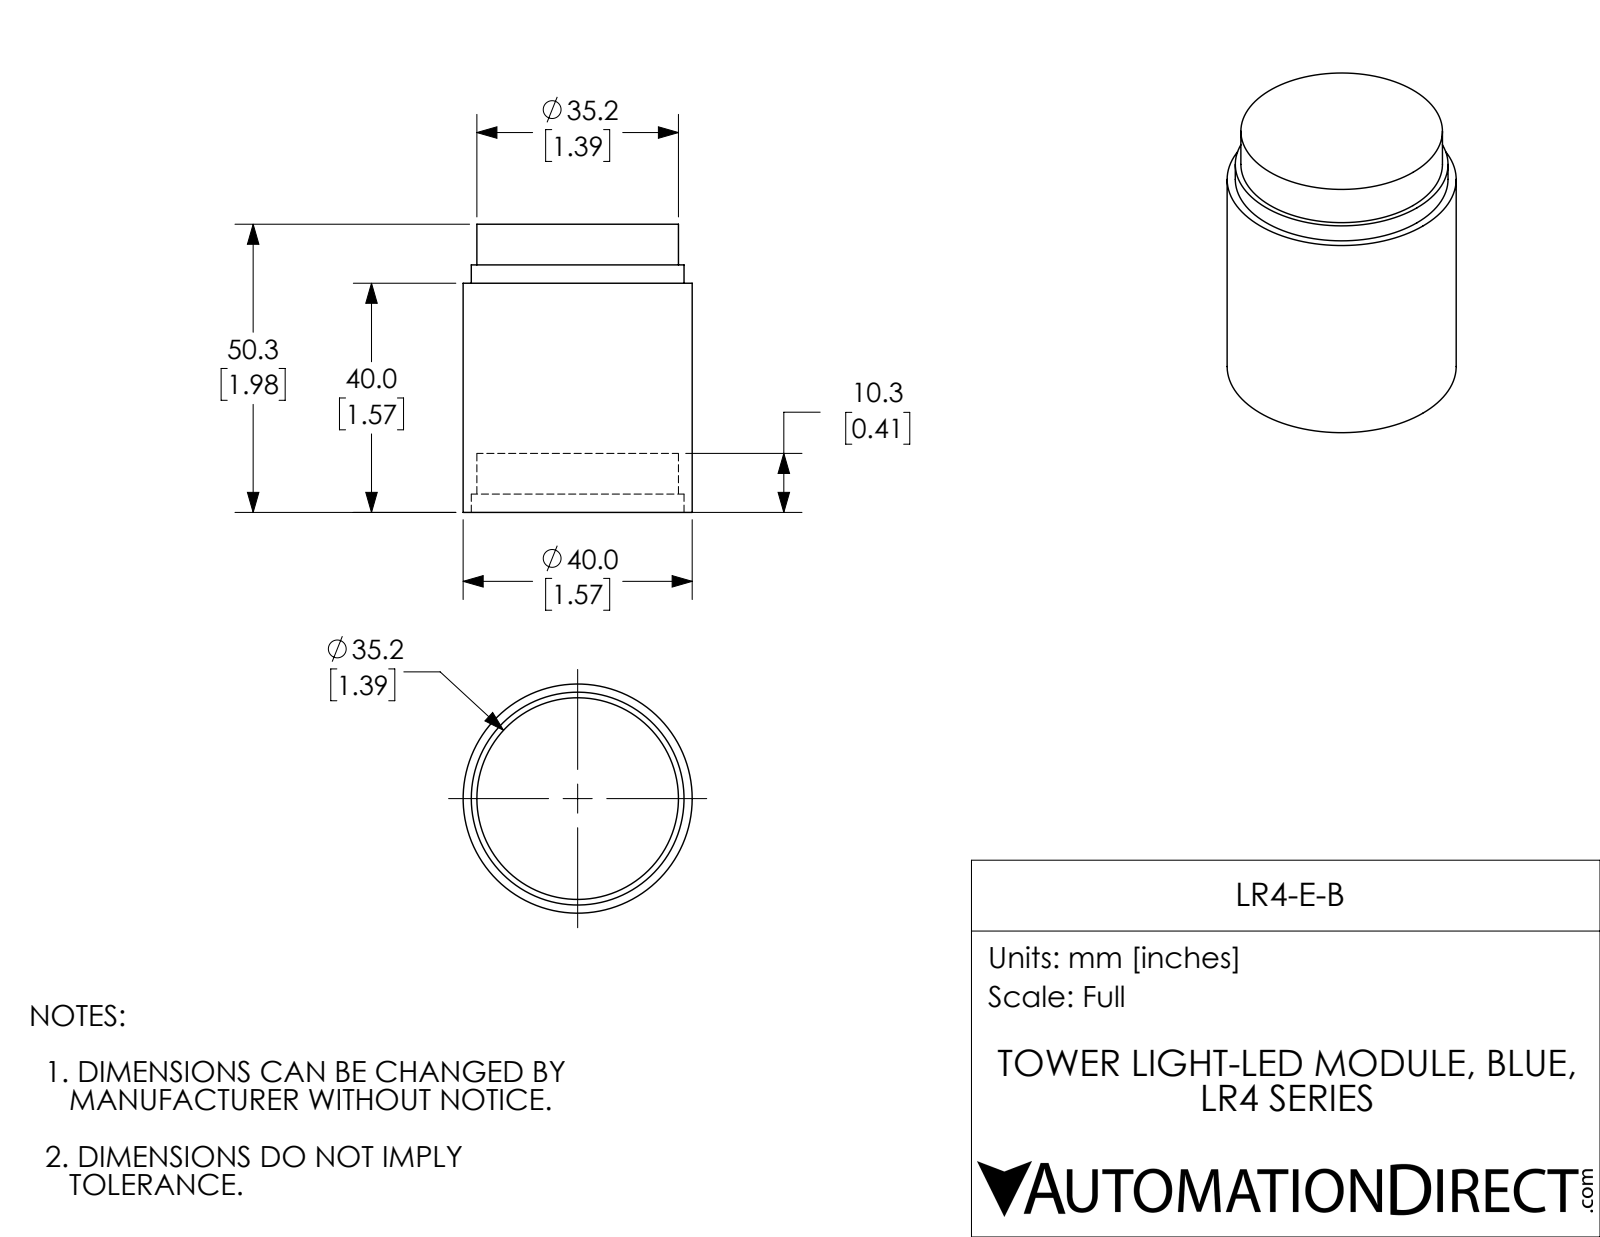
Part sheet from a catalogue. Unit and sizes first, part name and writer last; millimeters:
Units: millimetres
Overall size (bounding box): 50.3 × 40 × 40
Round holes (diameter × count): ⌀35.2 ×1, ⌀37.2 ×1
Round bosses / shafts (diameter × count): ⌀40 ×1
Main face-to-face distances: 40, 10.3, 3.2, 7.1, 50.3, 29.7, 43.2, 32.9, 36.8, 47.1
Volume: 50 260 mm³ · Surface area: 9 858 mm²
Bodies: 1 solid, 16 faces (6 planar, 10 cylindrical, 0 other)
Part name (STEP PRODUCT): LR4-E-B
STEP written by: SolidWorks 2017 (AUTOMOTIVE_DESIGN)
